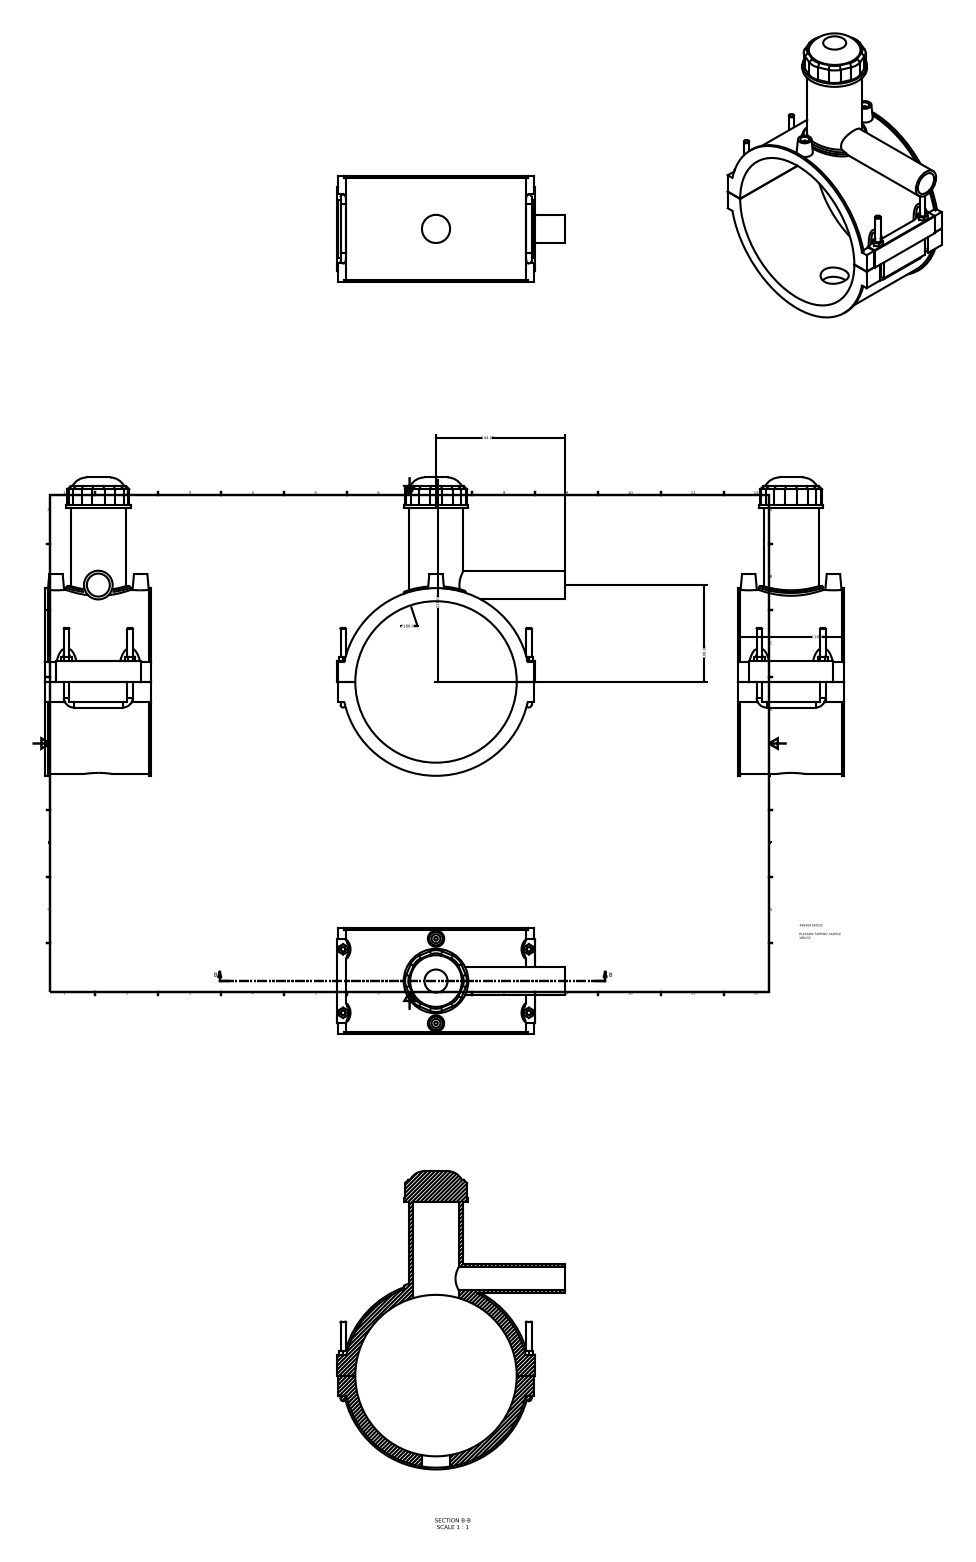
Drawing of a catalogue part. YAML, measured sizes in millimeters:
part_name: "496304180032"
step_written_by: "Autodesk Inventor 2015 (AUTOMOTIVE_DESIGN)"
units: millimeters
bodies: {solids: 1, faces: 181, planar: 110, cylindrical: 47, other: 24}
overall_size: [332.65, 254.5, 118]
volume: 1200000
surface_area: 250564
round_holes:
  - {diameter: 10, count: 2}
  - {diameter: 25.6, count: 1}
  - {diameter: 31.36, count: 1}
  - {diameter: 50.4, count: 1}
  - {diameter: 180, count: 1}
round_bosses_or_shafts:
  - {diameter: 6, count: 6}
  - {diameter: 4, count: 2}
  - {diameter: 209.3, count: 1}
  - {diameter: 205.2, count: 1}
  - {diameter: 72, count: 1}
  - {diameter: 61.2, count: 1}
  - {diameter: 32, count: 1}
partial_cylinders:
  - {radius: 18, count: 8}
  - {radius: 3, count: 4}
  - {radius: 7.5, count: 4}
  - {radius: 0.5, count: 1}
  - {radius: 106.7, count: 1}
face_to_face_distances: [118, 1, 220, 193.55, 193.45, 219, 22.45, 22.55, 2.36, 115.64]
hole_center_spacings: [47.2, 94.4]
